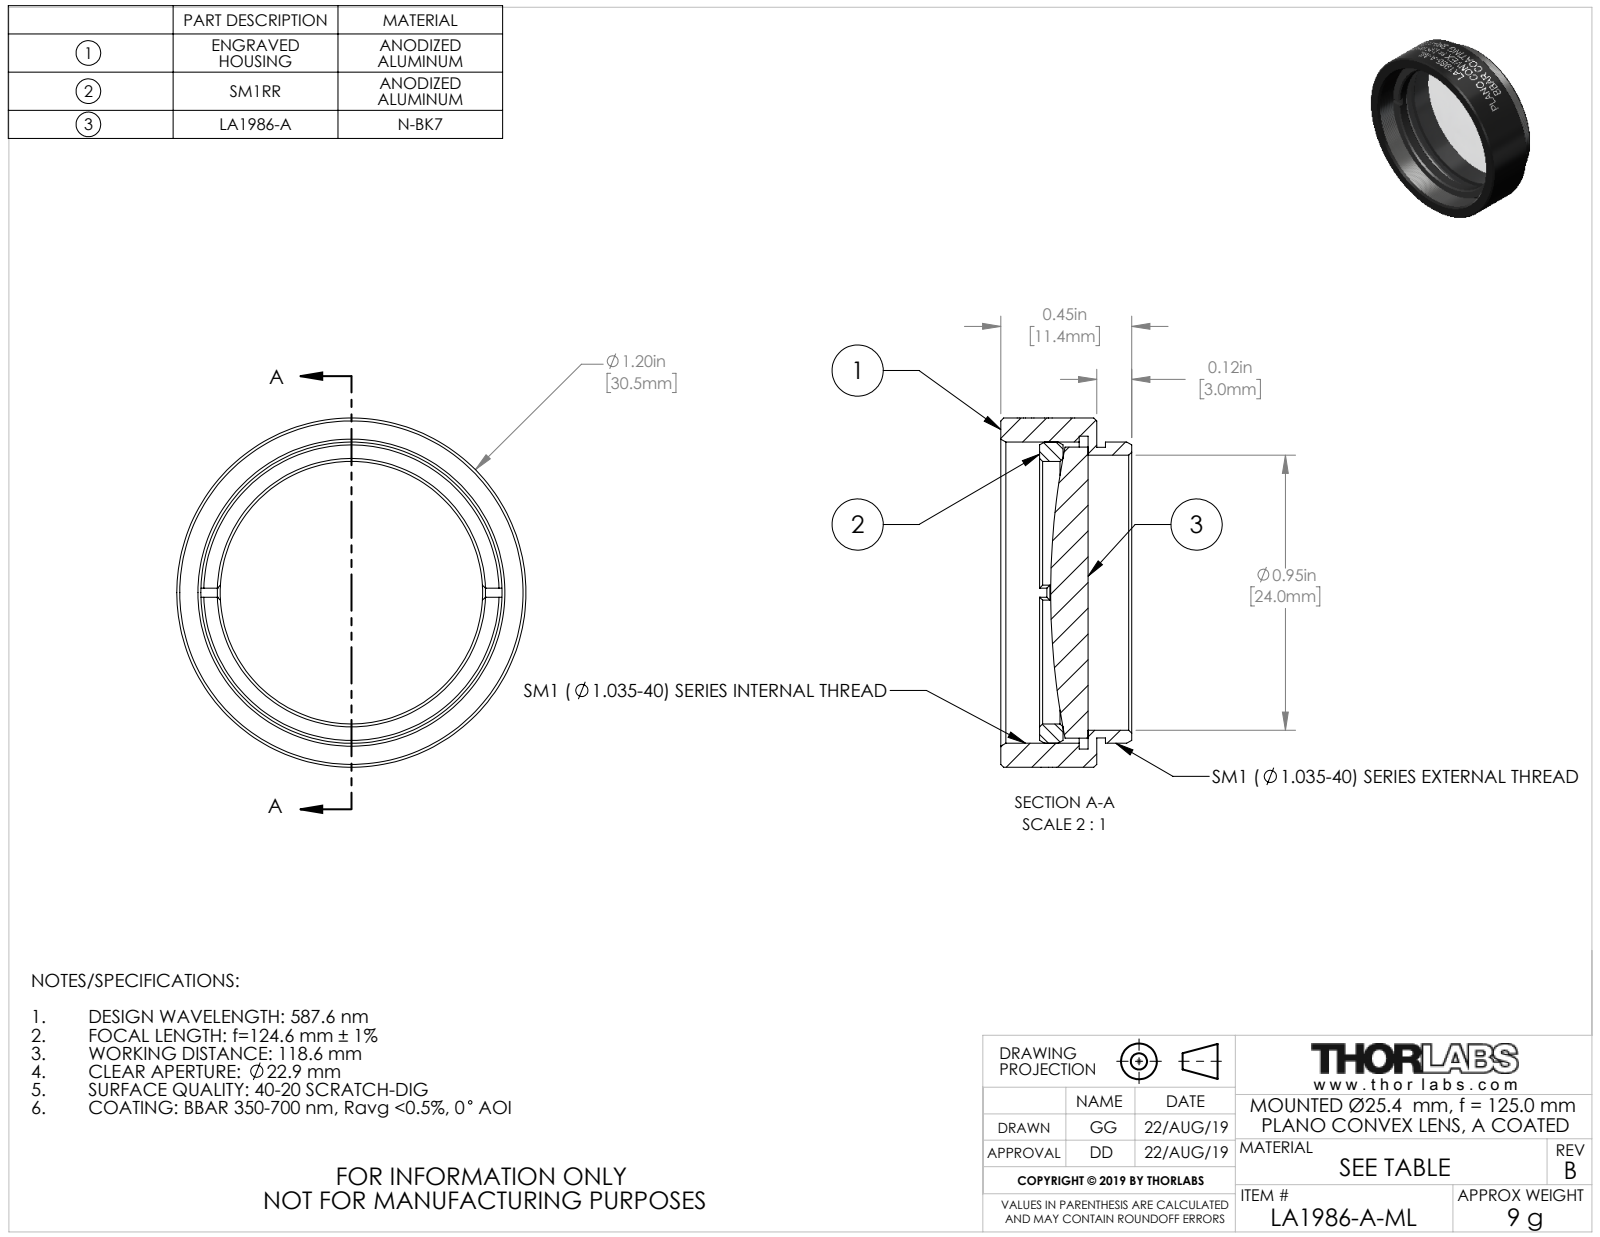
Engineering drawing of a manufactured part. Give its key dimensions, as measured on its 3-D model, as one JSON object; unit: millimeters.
{"part_name": "24443-E0W", "step_written_by": "SolidWorks 2018 (CONFIG_CONTROL_DESIGN)", "units": "millimeters", "bodies": {"solids": 3, "faces": 153, "planar": 20, "cylindrical": 109, "other": 24}, "overall_size": [30.48, 30.48, 11.43], "volume_mm3": 3414, "surface_area_mm2": 4317, "round_holes": [[22.91, 1], [24, 1], [27.3, 1]], "round_bosses_or_shafts": [[30.48, 1], [26.29, 1], [25.4, 1], [25.37, 1]], "face_to_face_distances": [0.76, 8.38, 7.62, 2.95, 2.19, 5.43, 4.98, 4.22, 2.03, 3.4]}
